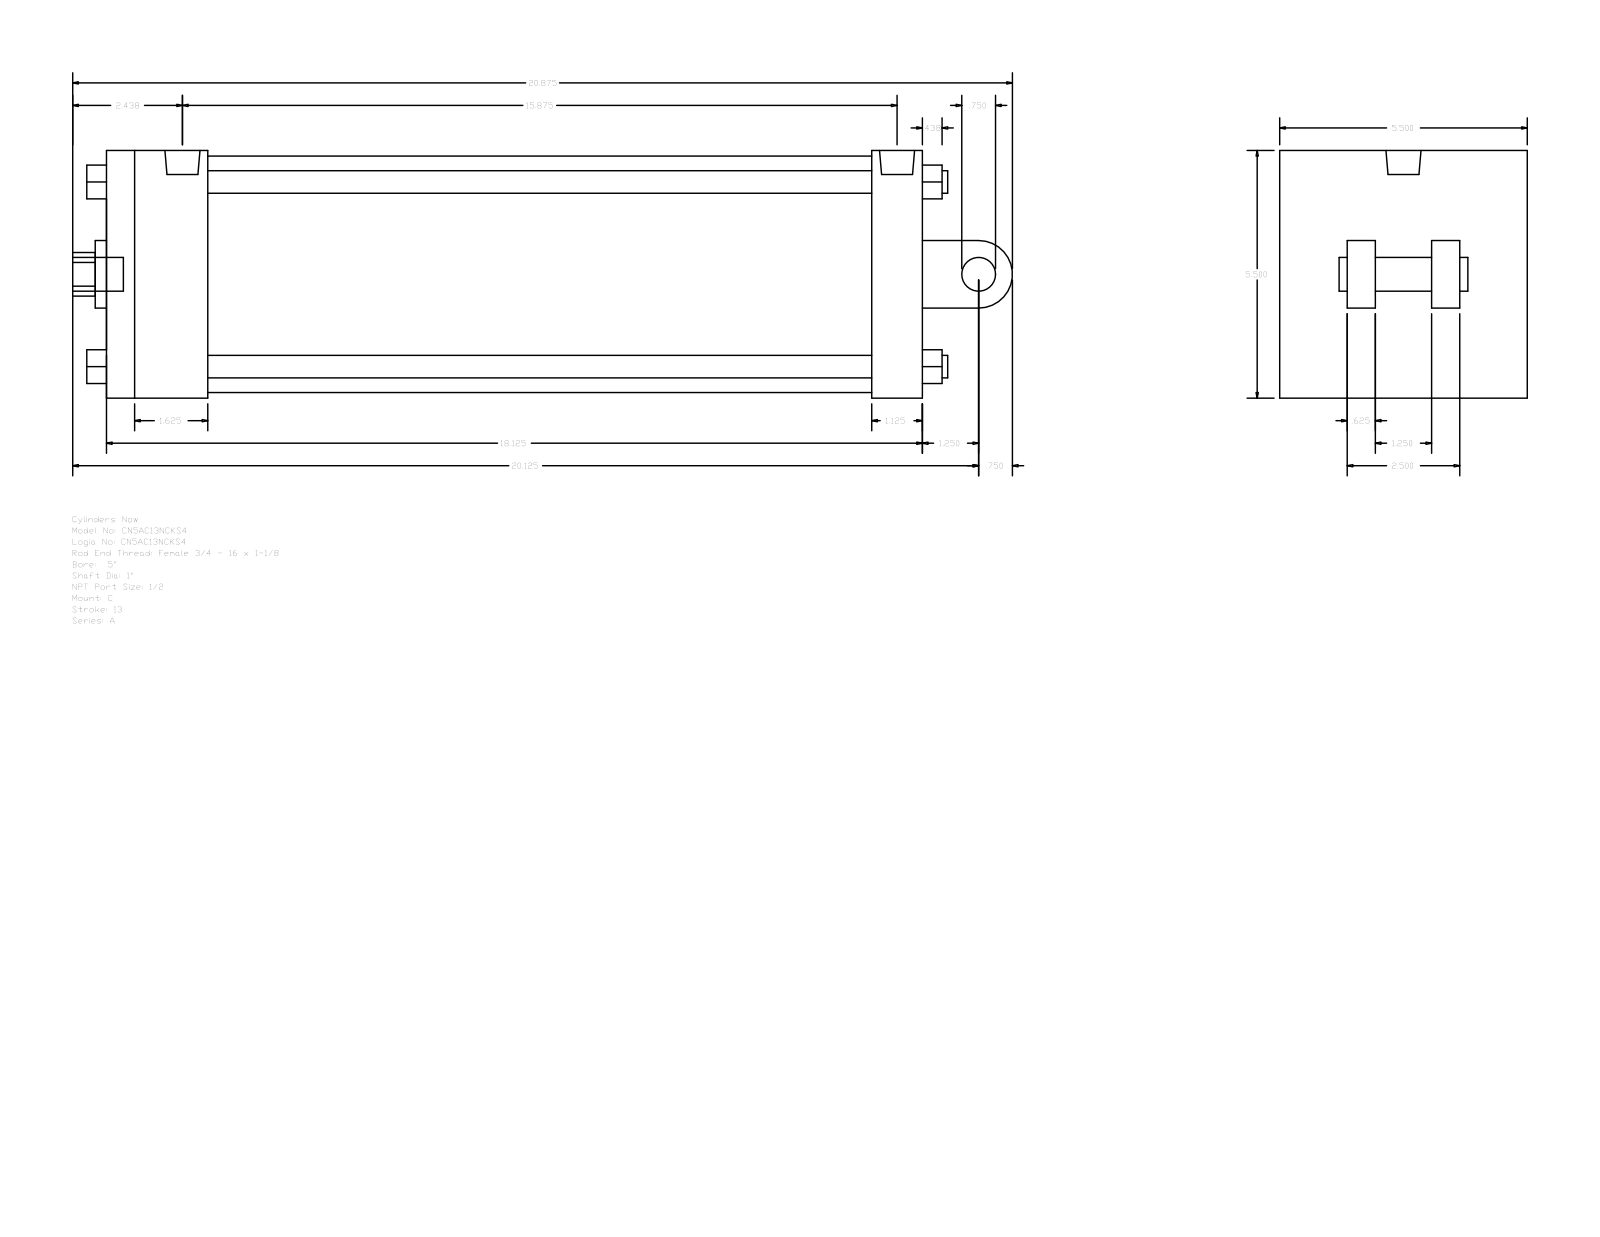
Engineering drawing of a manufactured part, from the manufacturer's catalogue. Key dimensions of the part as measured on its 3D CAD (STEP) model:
Part name (STEP PRODUCT): A_C__0500_1
STEP written by: GSSL Pune (CONFIG_CONTROL_DESIGN)
Units: millimetres
Bodies: 0 solids, 135 faces (102 planar, 33 cylindrical, 0 other)
Overall size (bounding box): 530.23 × 139.7 × 139.7
Round holes (diameter × count): ⌀8.73 ×2, ⌀19.77 ×1, ⌀25.4 ×1, ⌀38.1 ×1, ⌀133.35 ×1
Round bosses / shafts (diameter × count): ⌀12.7 ×4, ⌀19.05 ×2, ⌀8.73 ×2, ⌀19.77 ×1
Partial cylindrical surfaces — rounded edges, fillets, slot ends (radius × count): R12.29 ×1, R19.05 ×1
Main face-to-face distances: 139.7, 460.38, 57.15, 431.8, 374.65, 403.23, 28.58, 38.1, 15.87, 47.63
Hole centre spacings: 2.39
